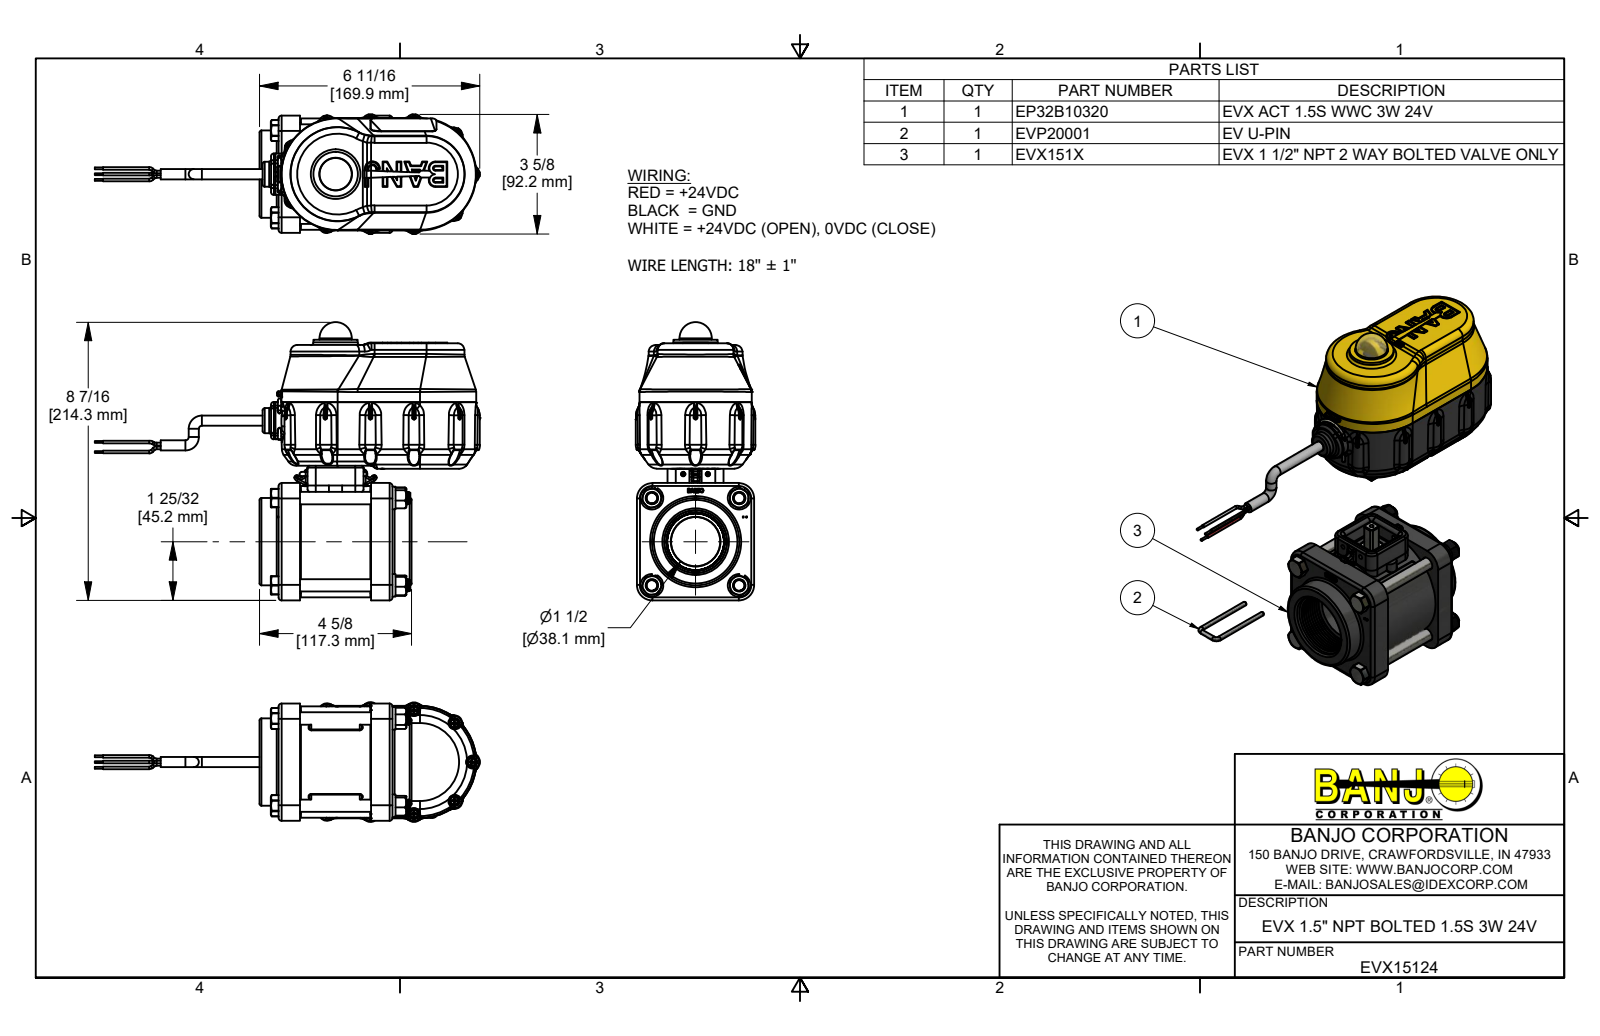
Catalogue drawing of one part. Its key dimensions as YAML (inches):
part_name: "EVX15124; EVX151X; MEVX20254A; MEVX20254AX (+8 more)"
step_written_by: "Autodesk Inventor 2019 (AUTOMOTIVE_DESIGN)"
units: inches
bodies: {solids: 96, faces: 11283, planar: 2908, cylindrical: 3323, other: 5052}
overall_size: [11.685, 8.437, 3.63]
volume: 61.51
surface_area: 654.1
round_holes:
  - {diameter: 0.095, count: 11}
  - {diameter: 0.15, count: 11}
  - {diameter: 0.08, count: 7}
  - {diameter: 0.107, count: 4}
  - {diameter: 0.126, count: 4}
  - {diameter: 0.136, count: 4}
  - {diameter: 0.148, count: 4}
  - {diameter: 0.15, count: 4}
  - {diameter: 0.17, count: 4}
  - {diameter: 0.307, count: 4}
  - {diameter: 0.385, count: 4}
  - {diameter: 0.406, count: 4}
round_bosses_or_shafts:
  - {diameter: 0.324, count: 60}
  - {diameter: 0.25, count: 17}
  - {diameter: 0.08, count: 15}
  - {diameter: 0.14, count: 11}
  - {diameter: 0.108, count: 11}
  - {diameter: 0.085, count: 11}
  - {diameter: 0.058, count: 6}
  - {diameter: 0.375, count: 5}
partial_cylinders:
  - {radius: 0.013, count: 180}
  - {radius: 0.04, count: 145}
  - {radius: 0.01, count: 84}
  - {radius: 0.02, count: 78}
  - {radius: 0.005, count: 53}
  - {radius: 0.03, count: 30}
  - {radius: 0.06, count: 28}
  - {radius: 0.08, count: 28}
face_to_face_distances: [0.1, 2.565, 0.06, 0.65, 2.808, 0.729, 0.211, 0.151, 1.896, 1.836]
hole_center_spacings: [1.872, 2.648, 2.69, 2.715, 1.662, 1.774, 2.088, 2.73]
